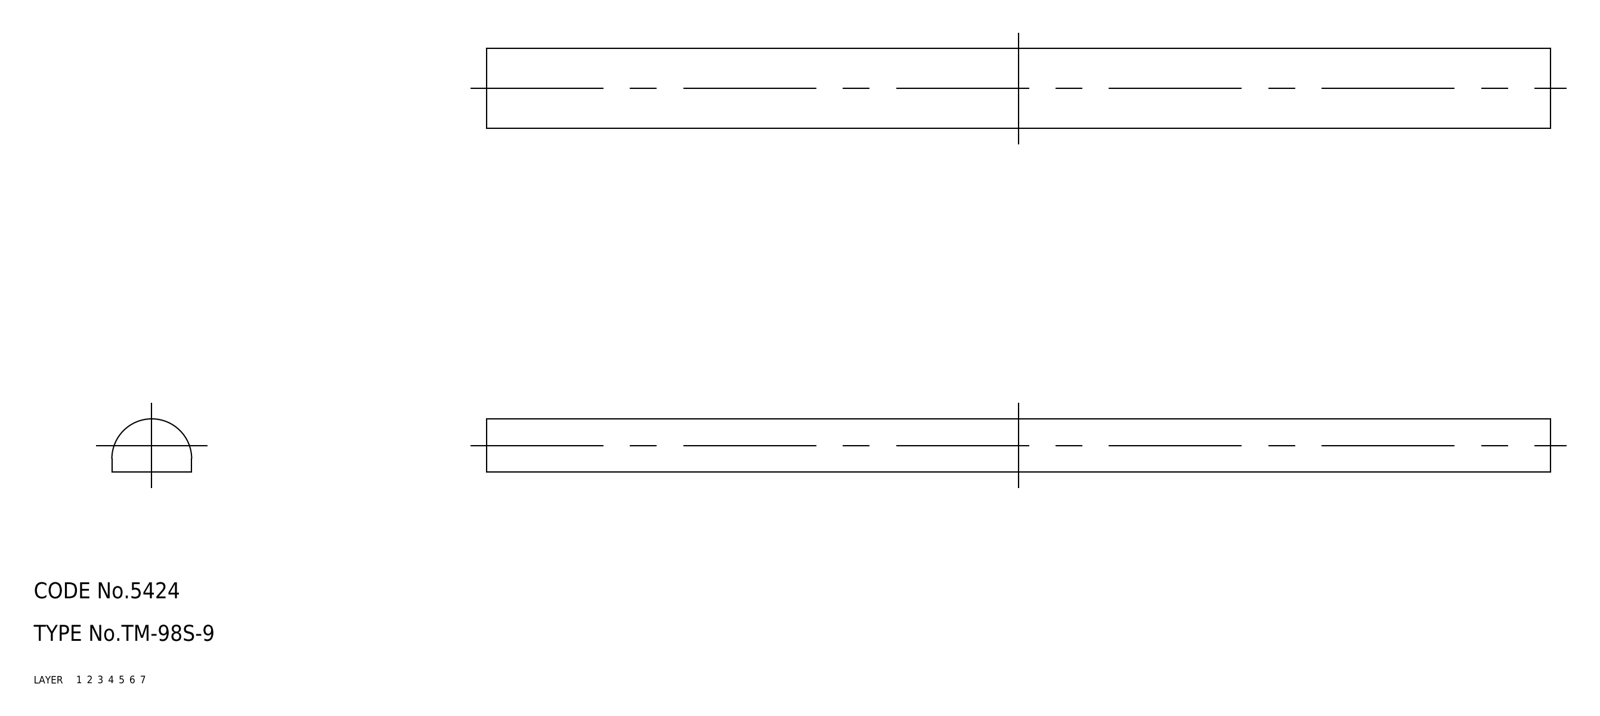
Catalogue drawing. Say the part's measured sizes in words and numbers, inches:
The part is named "rubber foam". Its 3-D file was written by "CADfix (AUTOMOTIVE_DESIGN)". It is 1 solid with 6 faces: 0 planar, 0 cylindrical and 6 other. Overall it measures 7.874 by 0.591 by 0.394 inches. Its volume is 1.536 cubic inches and its surface area 13.89 square inches.
